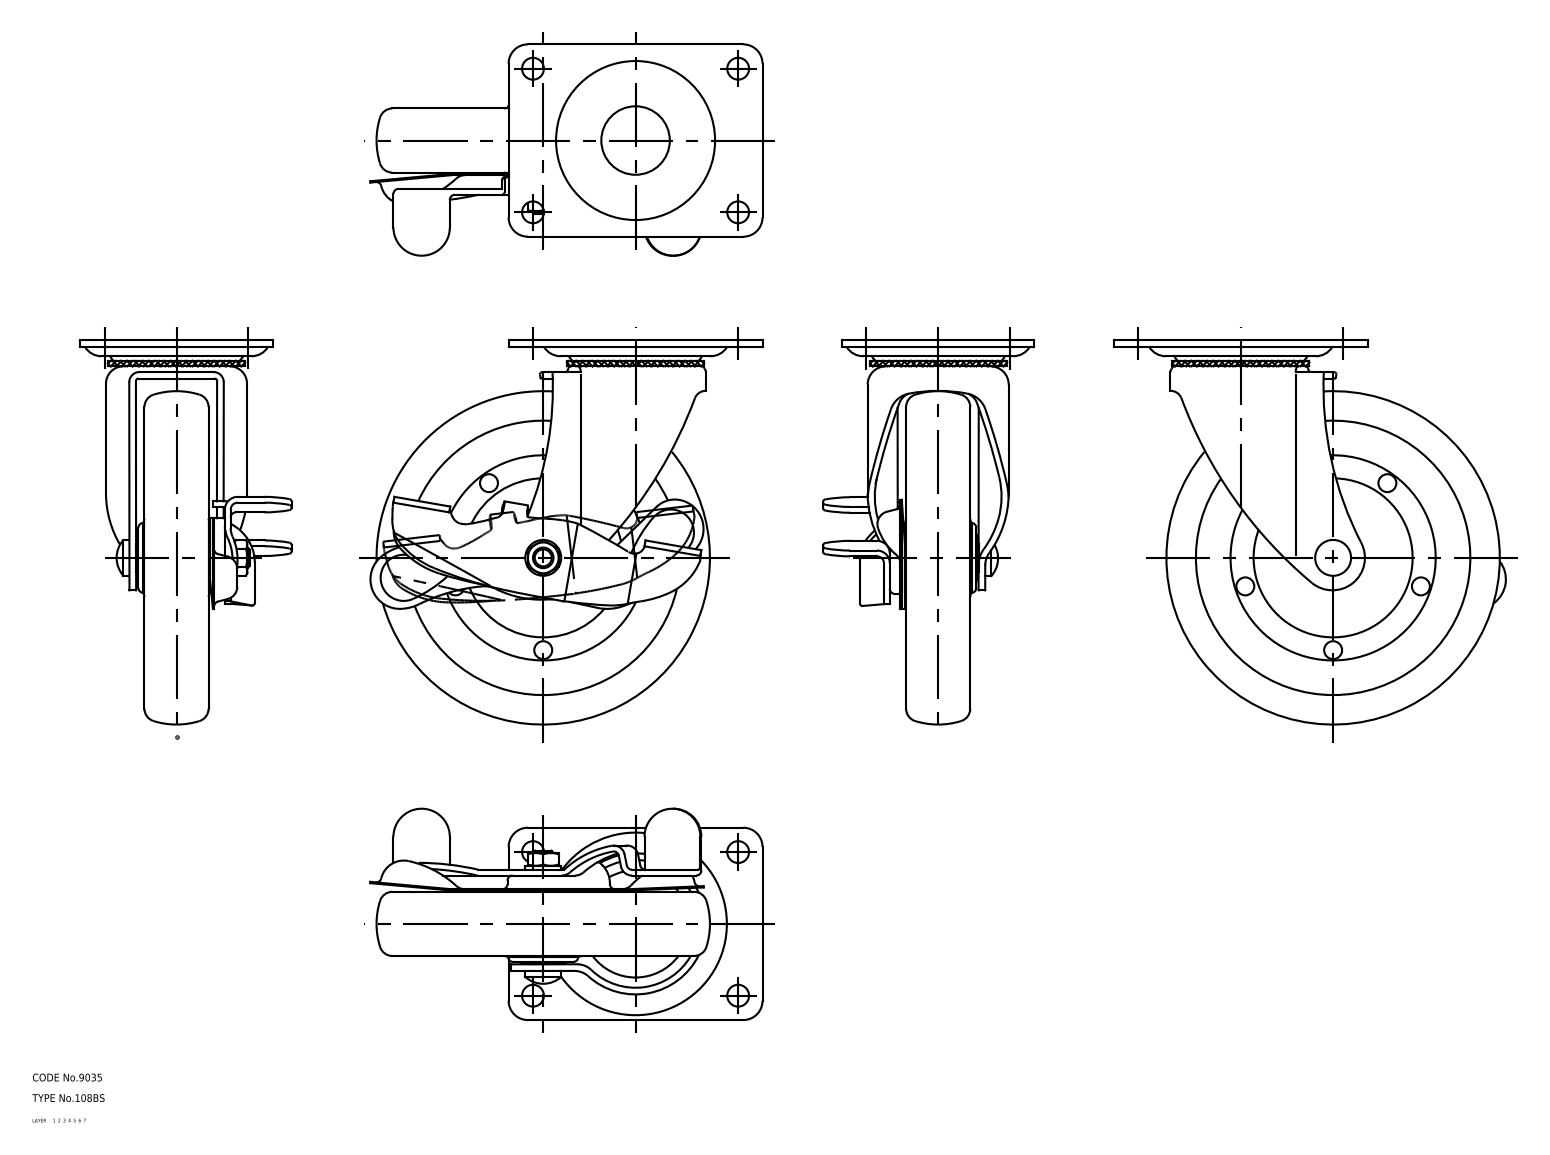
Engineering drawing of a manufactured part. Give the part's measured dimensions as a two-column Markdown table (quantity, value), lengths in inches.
| quantity | value |
| --- | --- |
| part name | lever; plate; wheel; mounting plate (+3 more) |
| STEP written by | CADfix (AUTOMOTIVE_DESIGN) |
| units | inches |
| bodies | 7 solids, 419 faces (0 planar, 0 cylindrical, 419 other) |
| overall size | 6.019 × 5.906 × 3.244 |
| volume | 21.96 in³ |
| surface area | 152.6 in² |
